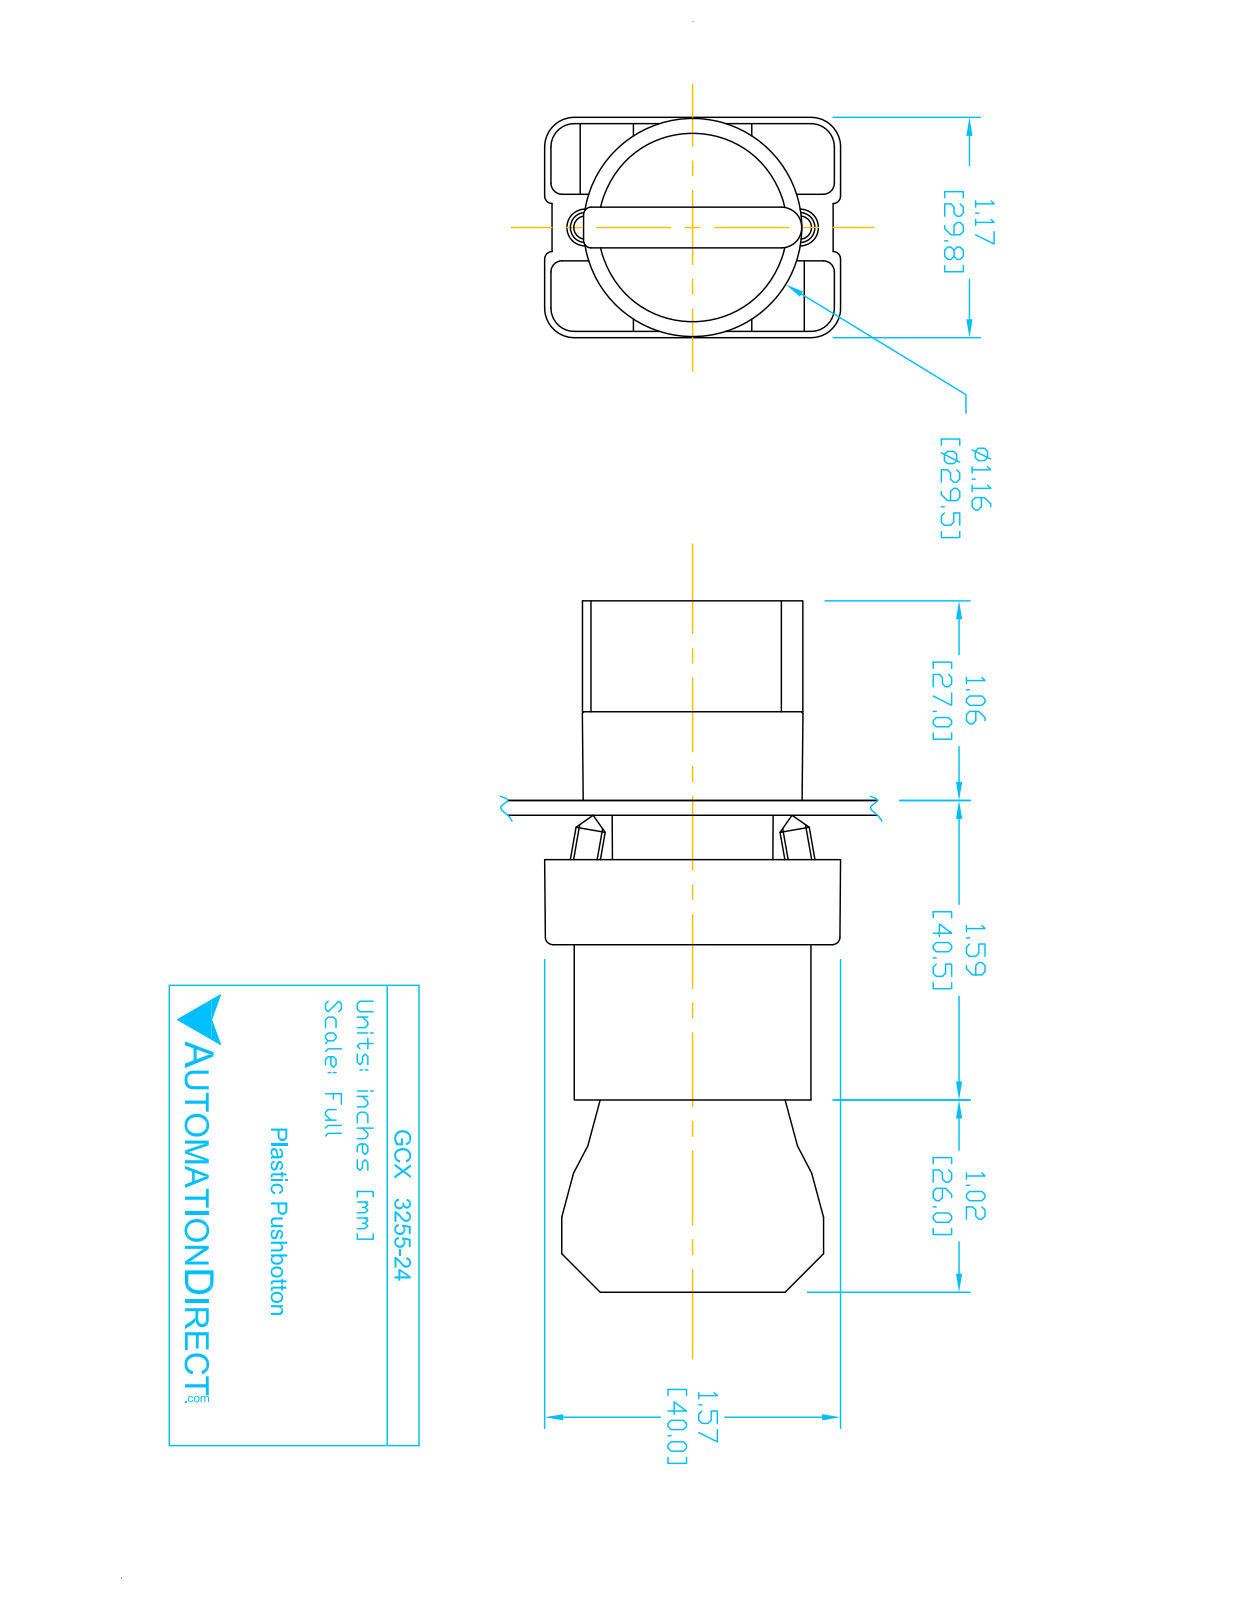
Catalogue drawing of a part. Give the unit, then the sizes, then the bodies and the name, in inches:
Units: inches
Overall size (bounding box): 3.653 × 1.581 × 1.177
Round holes (diameter × count): ⌀0.079 ×2, ⌀0.124 ×2, ⌀0.13 ×2, ⌀0.087 ×1, ⌀0.197 ×1, ⌀0.469 ×1, ⌀0.878 ×1, ⌀0.888 ×1, ⌀1.024 ×1
Round bosses / shafts (diameter × count): ⌀0.157 ×4, ⌀1.175 ×1, ⌀1.004 ×1, ⌀0.945 ×1, ⌀0.856 ×1, ⌀0.78 ×1, ⌀0.504 ×1
Partial cylindrical surfaces — rounded edges, fillets, slot ends (radius × count): R0.059 ×24, R0.041 ×12, R0.124 ×12, R0.157 ×12, R0.039 ×9, R0.128 ×2, R0.02 ×1, R0.063 ×1
Main face-to-face distances: 0.827, 2.02, 1.193, 0.579, 1.244, 1.171, 0.472, 0.469, 0.031, 0.033
Hole centre spacings: 0.236, 0.544, 0.472, 0.49
Volume: 2.799 in³ · Surface area: 39 in²
Bodies: 8 solids, 445 faces (263 planar, 151 cylindrical, 31 other)
Part name (STEP PRODUCT): ECX3029-2; ecx1040; GCX3255-24; GCX3255 OPERATOR (+1 more)
STEP written by: SolidWorks 2016 (AUTOMOTIVE_DESIGN)
